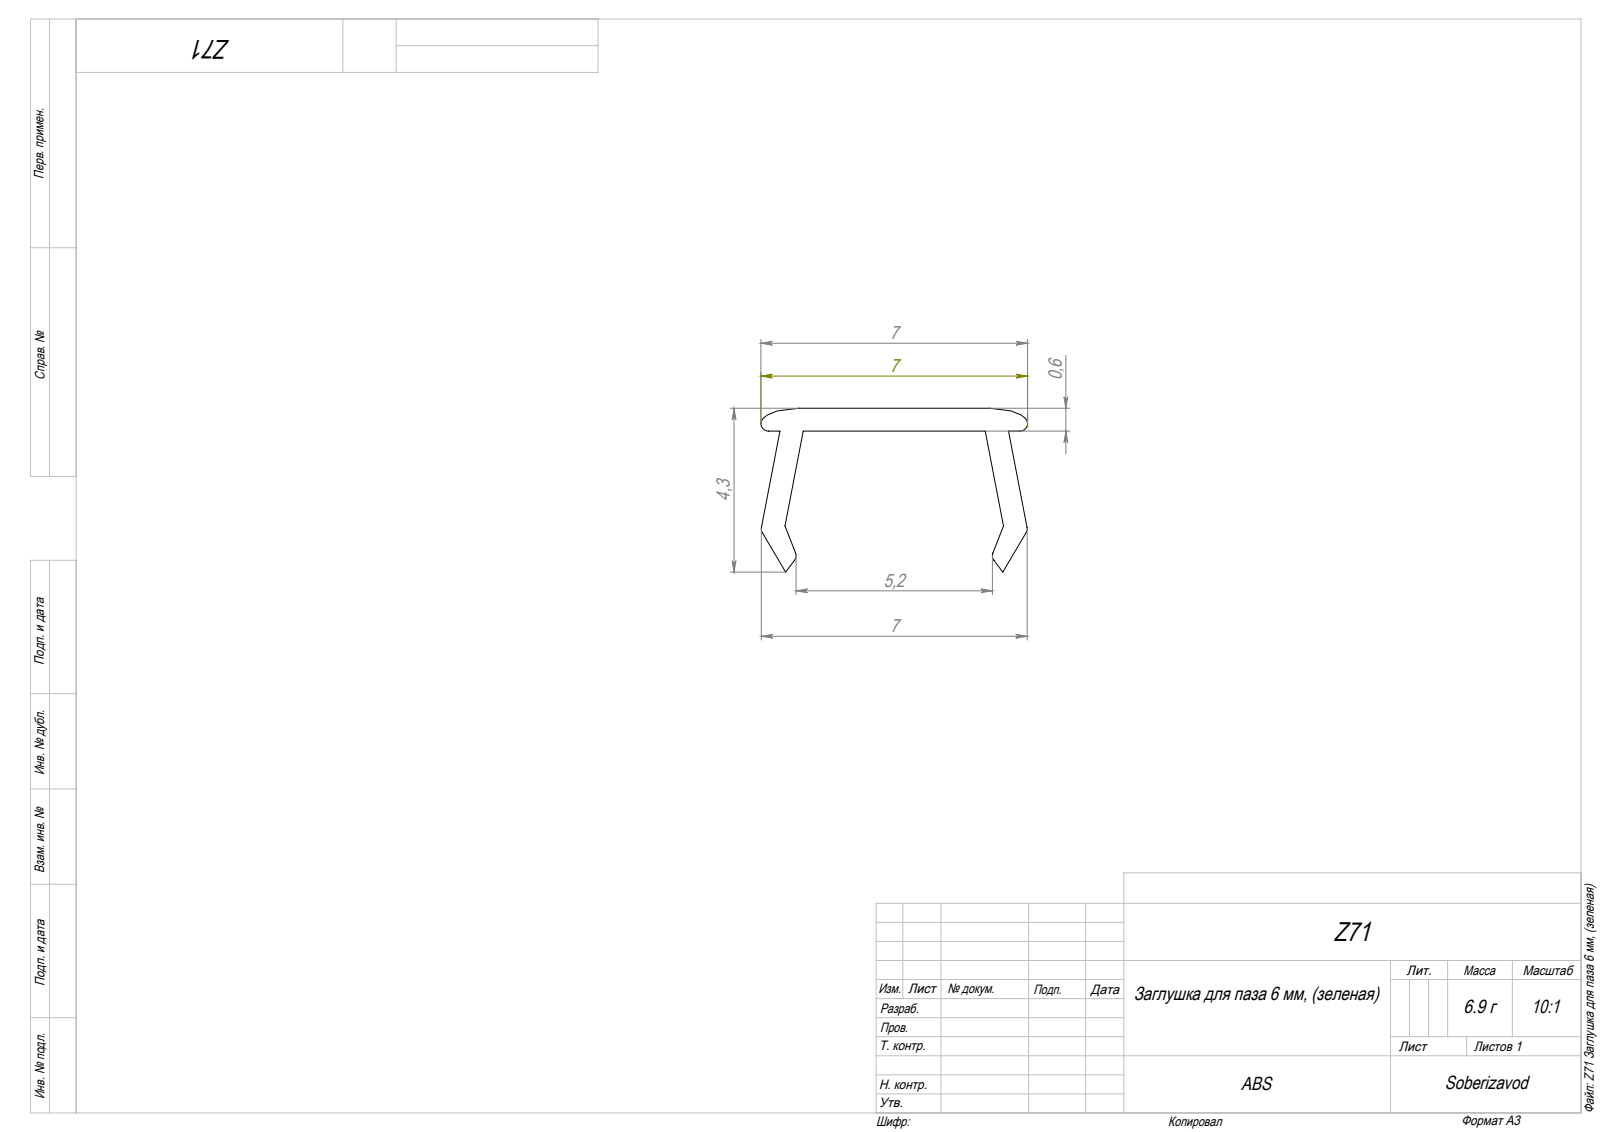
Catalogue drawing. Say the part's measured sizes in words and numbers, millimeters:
The part is named "Z71 Заглушка для паза 6 мм, (зеленая)". Its 3-D file was written by "SolidWorks 2025 (AUTOMOTIVE_DESIGN)". It is 1 solid with 26 faces: 16 planar, 8 cylindrical and 2 other. Overall it measures 1000 by 7 by 4.3 millimeters. Its volume is 8 251 cubic millimeters and its surface area 28 934 square millimeters. Partial cylindrical surfaces (rounded edges, fillets, slot ends): 6 of radius 0.2. The main face-to-face distances are 0.6, 1000.
